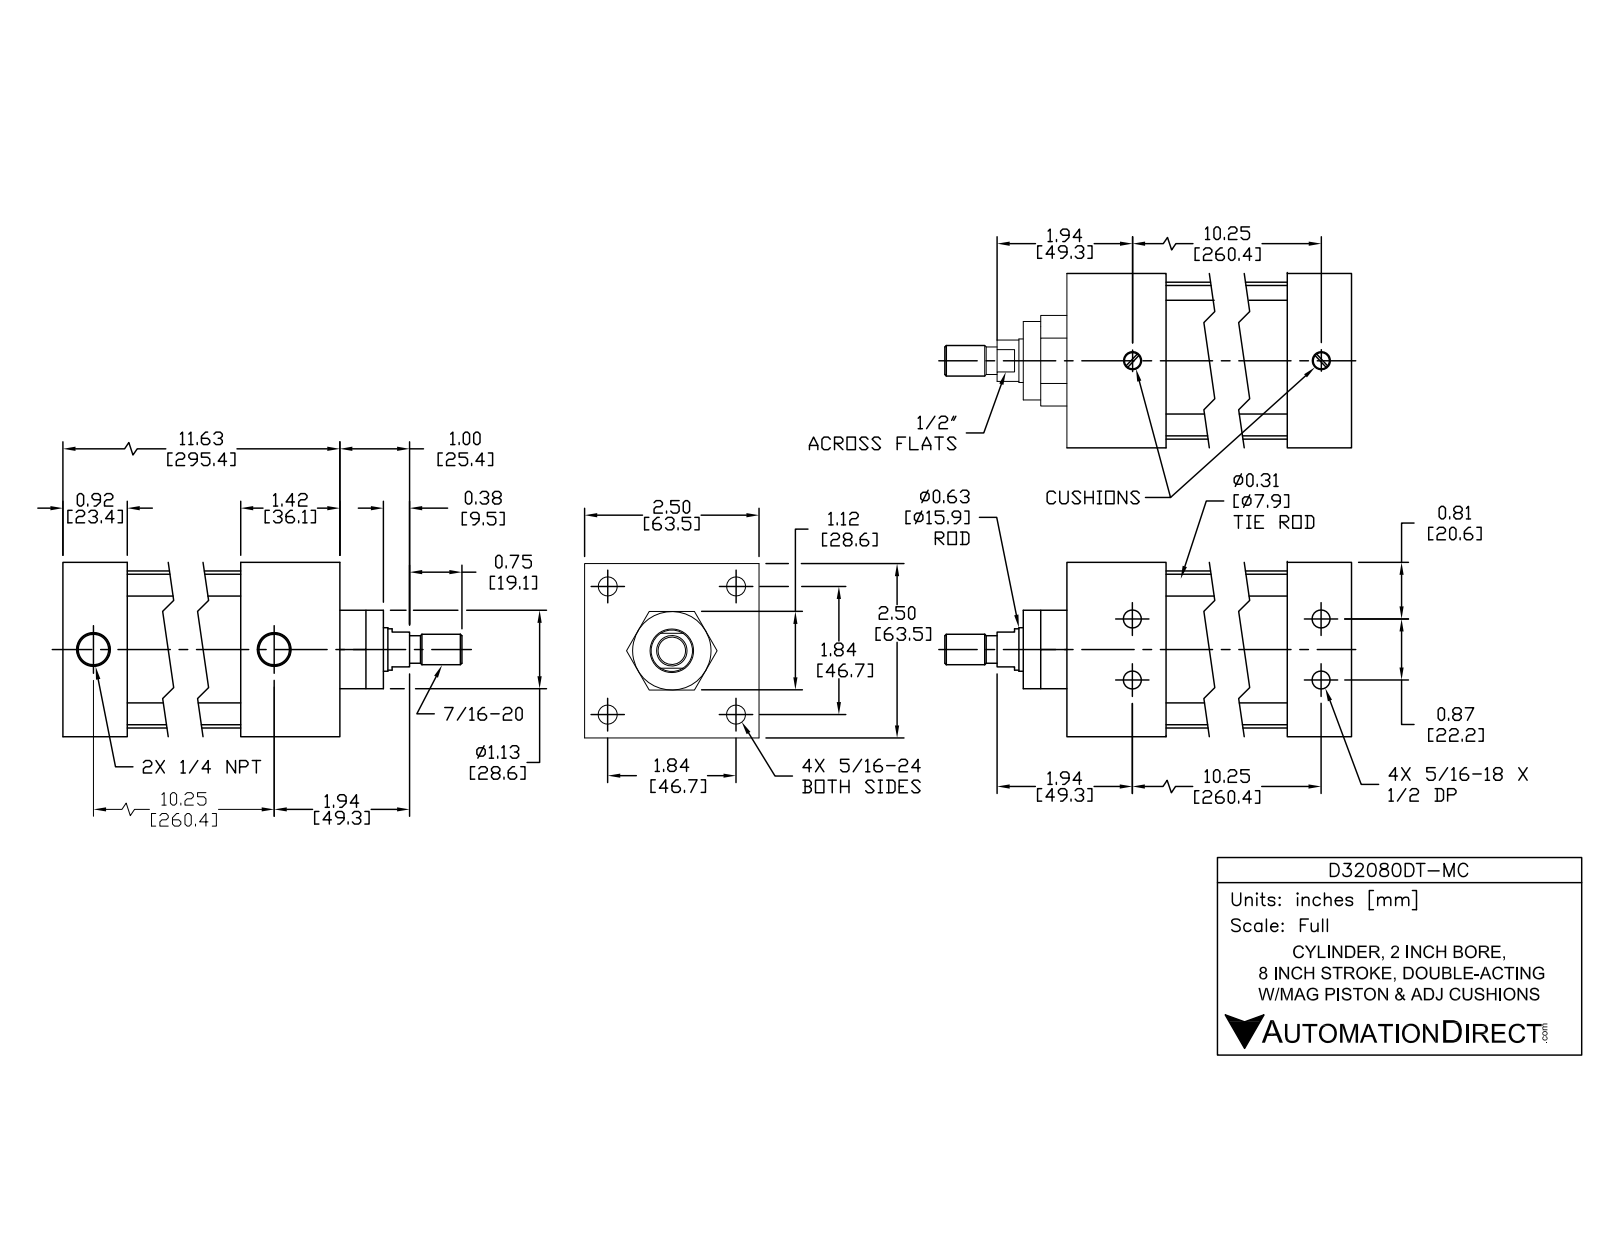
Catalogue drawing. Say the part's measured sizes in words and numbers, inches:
The part is named "D32080DT-M BODY; D32080DT-MC; D32080DT-M PISTON". Its 3-D file was written by "SolidWorks 2015 (AUTOMOTIVE_DESIGN)". It is 12 solids with 298 faces: 94 planar, 114 cylindrical and 90 other. Overall it measures 13.371 by 2.5 by 2.5 inches. Its volume is 30.94 cubic inches and its surface area 274.3 square inches. Round holes: 4 of diameter 0.252, 4 of diameter 0.267, 4 of diameter 0.359, 4 of diameter 0.5, 2 of diameter 0.297, 2 of diameter 0.477, 1 of diameter 0.625, 1 of diameter 0.628, 1 of diameter 2. Round bosses or shafts: 4 of diameter 0.484, 4 of diameter 0.313, 4 of diameter 0.282, 1 of diameter 2.25, 1 of diameter 1.997, 1 of diameter 1.12, 1 of diameter 0.622, 1 of diameter 0.59. Partial cylindrical surfaces (rounded edges, fillets, slot ends): 4 of radius 0.25. The main face-to-face distances are 2.5, 11.621, 1.42, 10.201, 9.281, 10.701, 0.92, 1, 10.601, 9.181. The hole center spacings are 0.437, 1.307, 1.848, 10.254, 10.245, 0.875, 2.613, 10.282.
